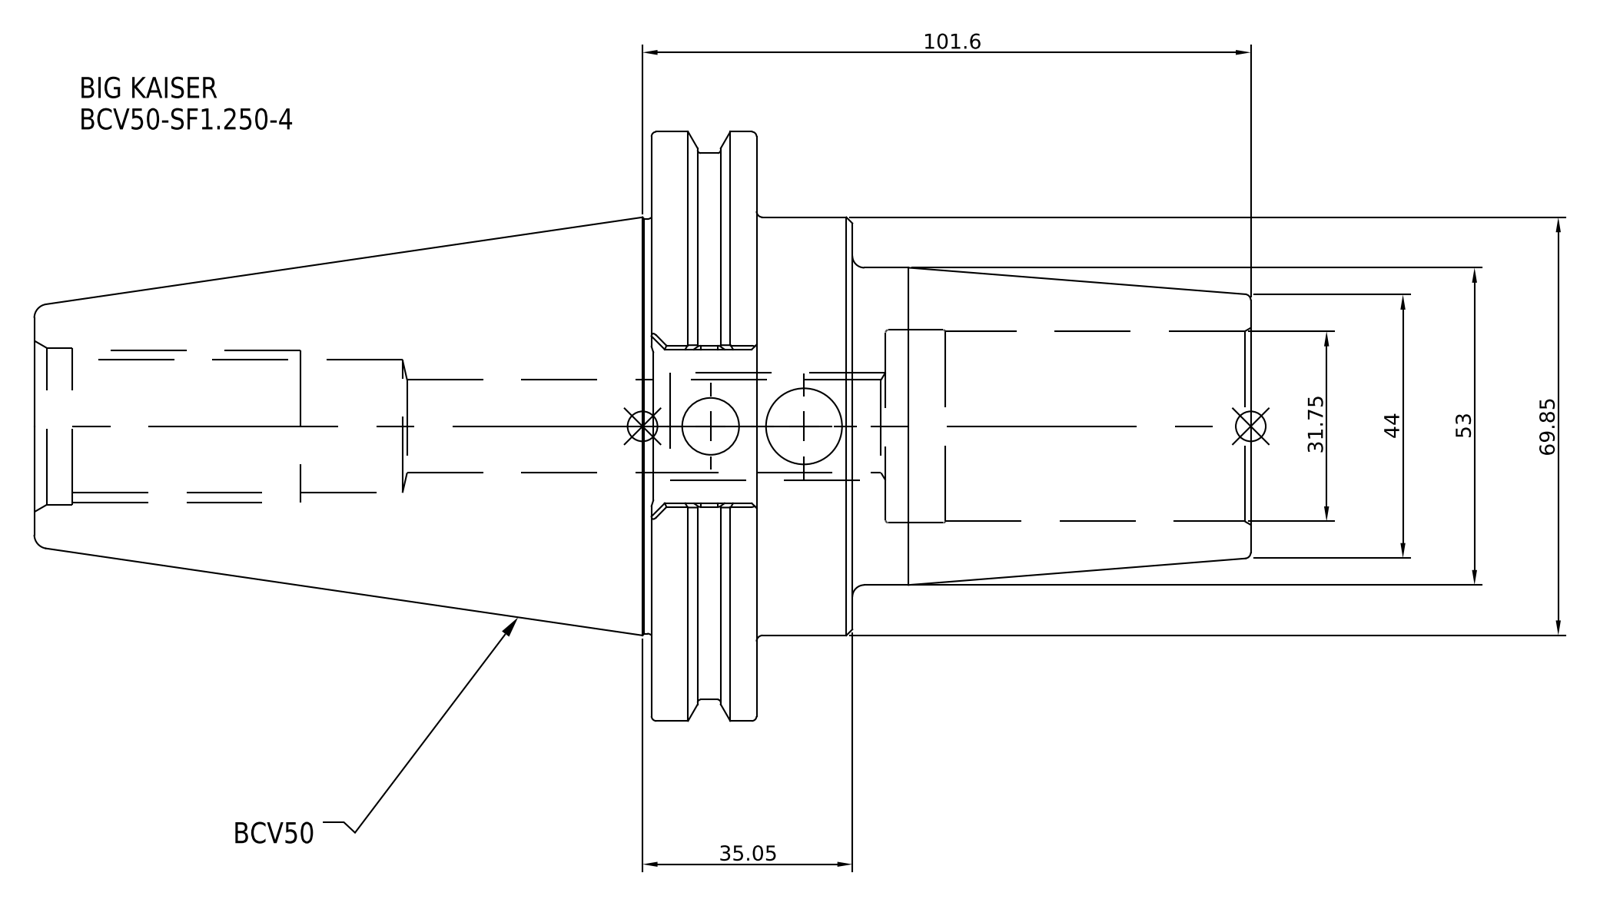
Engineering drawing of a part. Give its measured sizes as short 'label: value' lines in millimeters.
name: BCV50-SF1_250-4
written by: SolidWorks 2021 (CONFIG_CONTROL_DESIGN)
unit: mm
bodies: 1 solid, 30 faces (8 planar, 14 cylindrical, 8 other)
size: 203.2 × 98.43 × 98.43
volume: 528 907 mm³; area: 55 685 mm²
holes: 1× ⌀31.75
bosses: 1× ⌀98.43, 1× ⌀91.29, 1× ⌀69.85, 1× ⌀53
face distances: 17.55, 16, 33.55, 136.65, 120.65, 103.1, 15.55, 31.55, 49.1, 152.2
